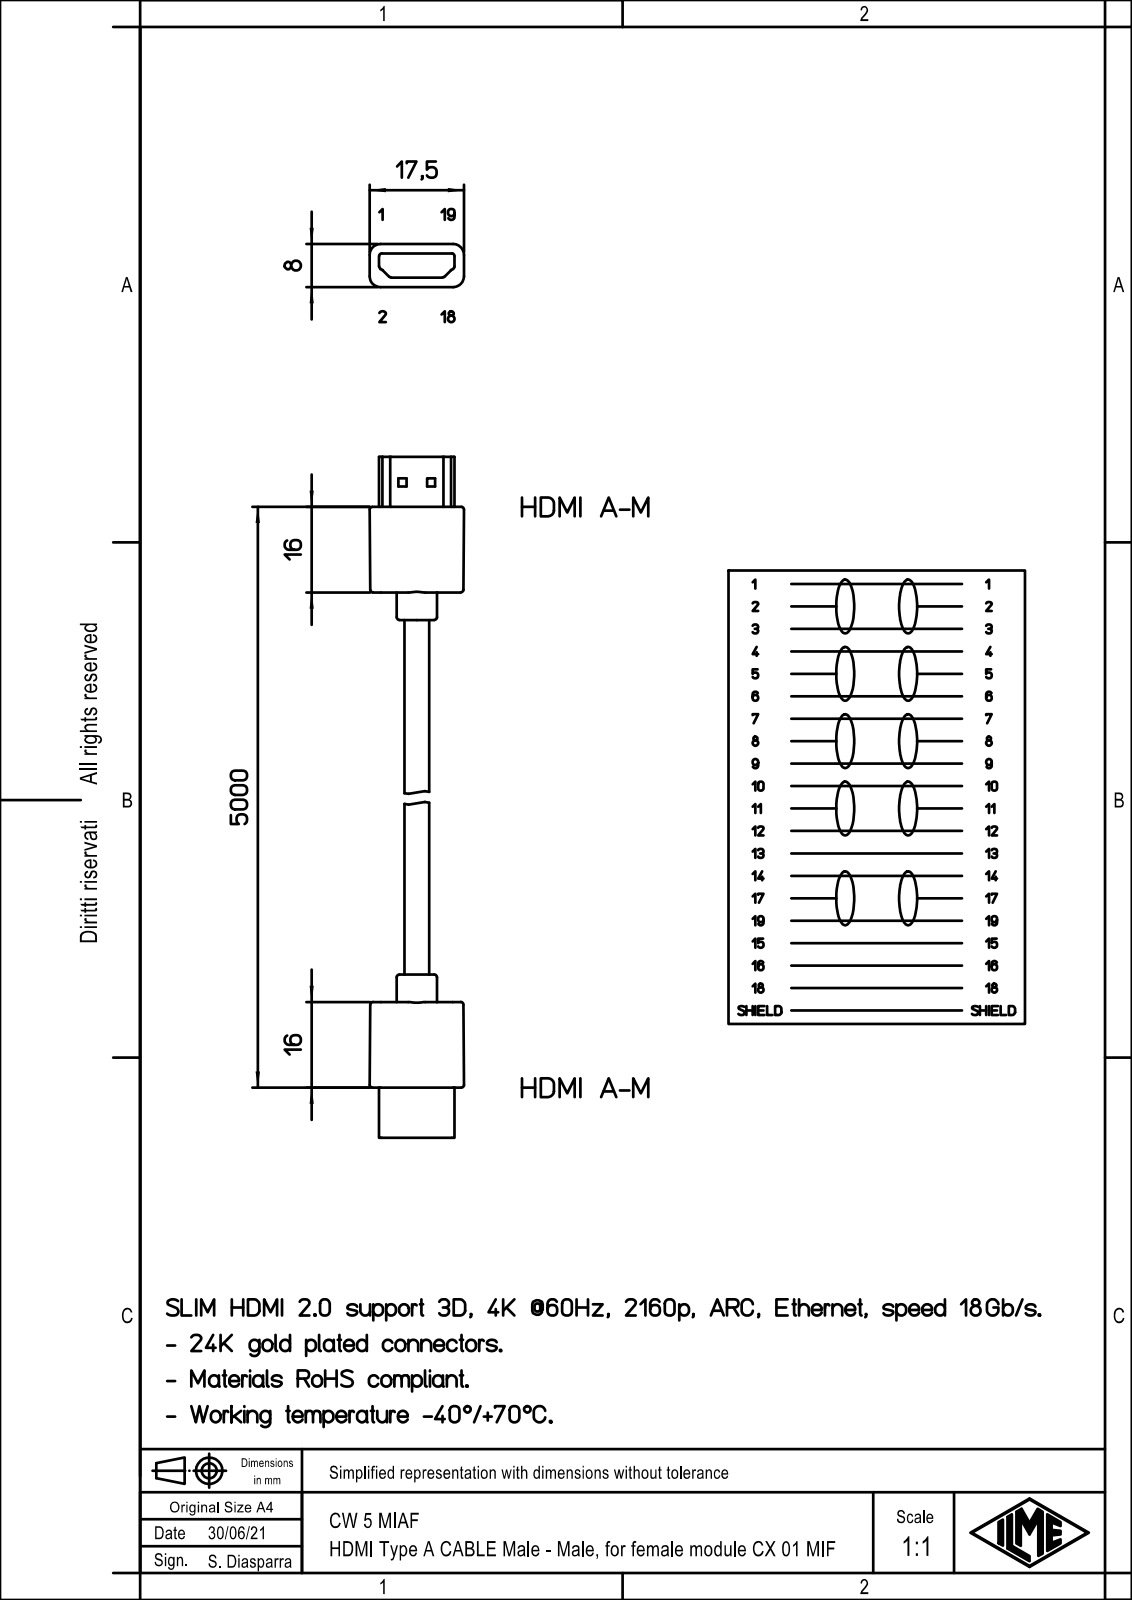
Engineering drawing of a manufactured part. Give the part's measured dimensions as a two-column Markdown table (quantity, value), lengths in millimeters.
| quantity | value |
| --- | --- |
| part name | CW_5_MIAF |
| STEP written by | Creo Elements/Direct Modeling 20.1B 02-Apr-2019 (C) Parametric Technology GmbH (AUTOMOTIVE_DESIGN) |
| units | millimeters |
| bodies | 1 solid, 82 faces (52 planar, 30 cylindrical, 0 other) |
| overall size | 138.6 × 17.5 × 8 |
| volume | 7 201 mm³ |
| surface area | 4 044 mm² |
| round bosses / shafts (diameter × count) | 7.5 × 1, 4.6 × 1 |
| partial cylindrical surfaces (radius × count) | 0.5 × 6, 2 × 4, 0.4 × 2 |
| main face-to-face distances | 1.75, 8, 6.25, 4.5, 16, 104, 17.5, 9.3, 25.3, 113.3 |
